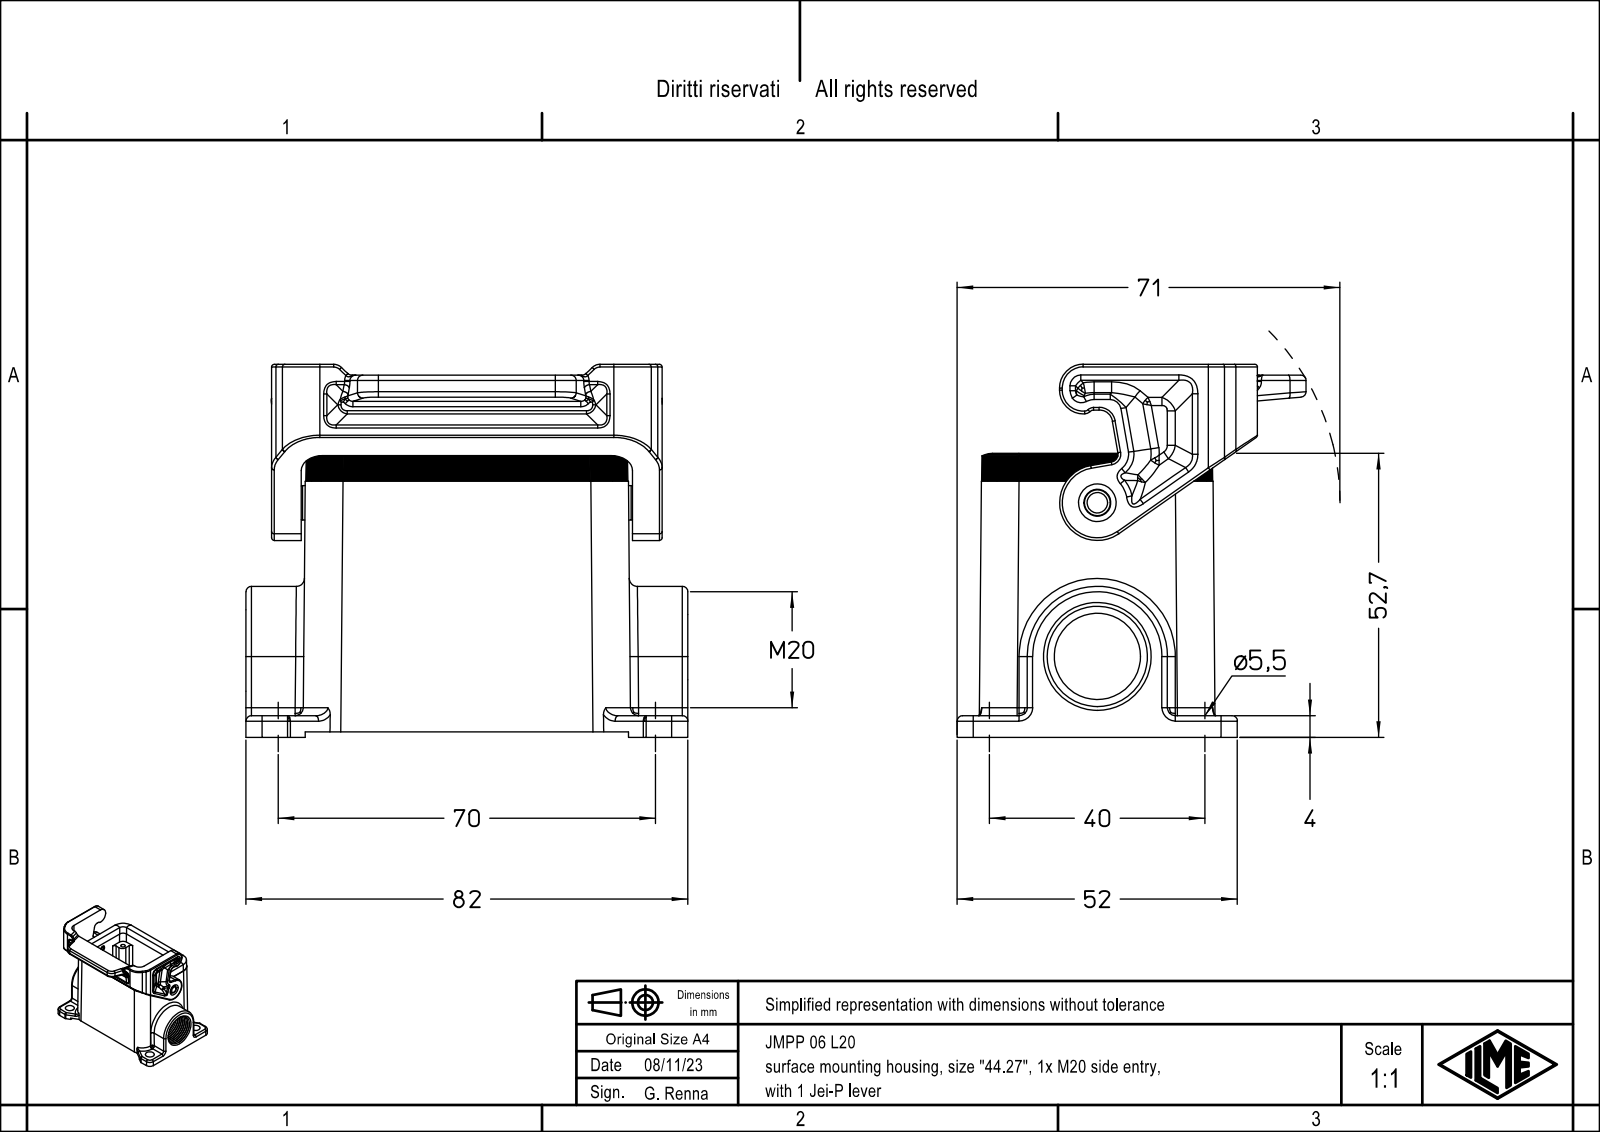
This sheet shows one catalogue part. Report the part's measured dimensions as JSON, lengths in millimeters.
{"part_name": "JMPP_06_L20", "step_written_by": "PTC Creo Elements/Direct Modeling 19.0E 27-Jun-2016 (C) Parametric Technology GmbH (AUTOMOTIVE_DESIGN)", "units": "millimeters", "bodies": {"solids": 1, "faces": 377, "planar": 237, "cylindrical": 132, "other": 8}, "overall_size": [82, 67.4, 61.3], "volume_mm3": 77267, "surface_area_mm2": 39991, "round_holes": [[3.1, 4], [5, 4], [5.5, 4], [10.2, 1], [16, 1], [20, 1]], "round_bosses_or_shafts": [[7.2, 1]], "partial_cylinders_radius": [[3, 14], [2, 8], [7, 5], [1, 2], [1.5, 2], [1.01, 1], [2.4, 1], [3.5, 1]], "face_to_face_distances": [3, 2, 4, 50.15, 11.85, 62, 6, 9, 67, 52], "hole_center_spacings": [2.92, 12.18, 14.53, 29.54, 35.93, 37.79, 45.57, 54.23]}
